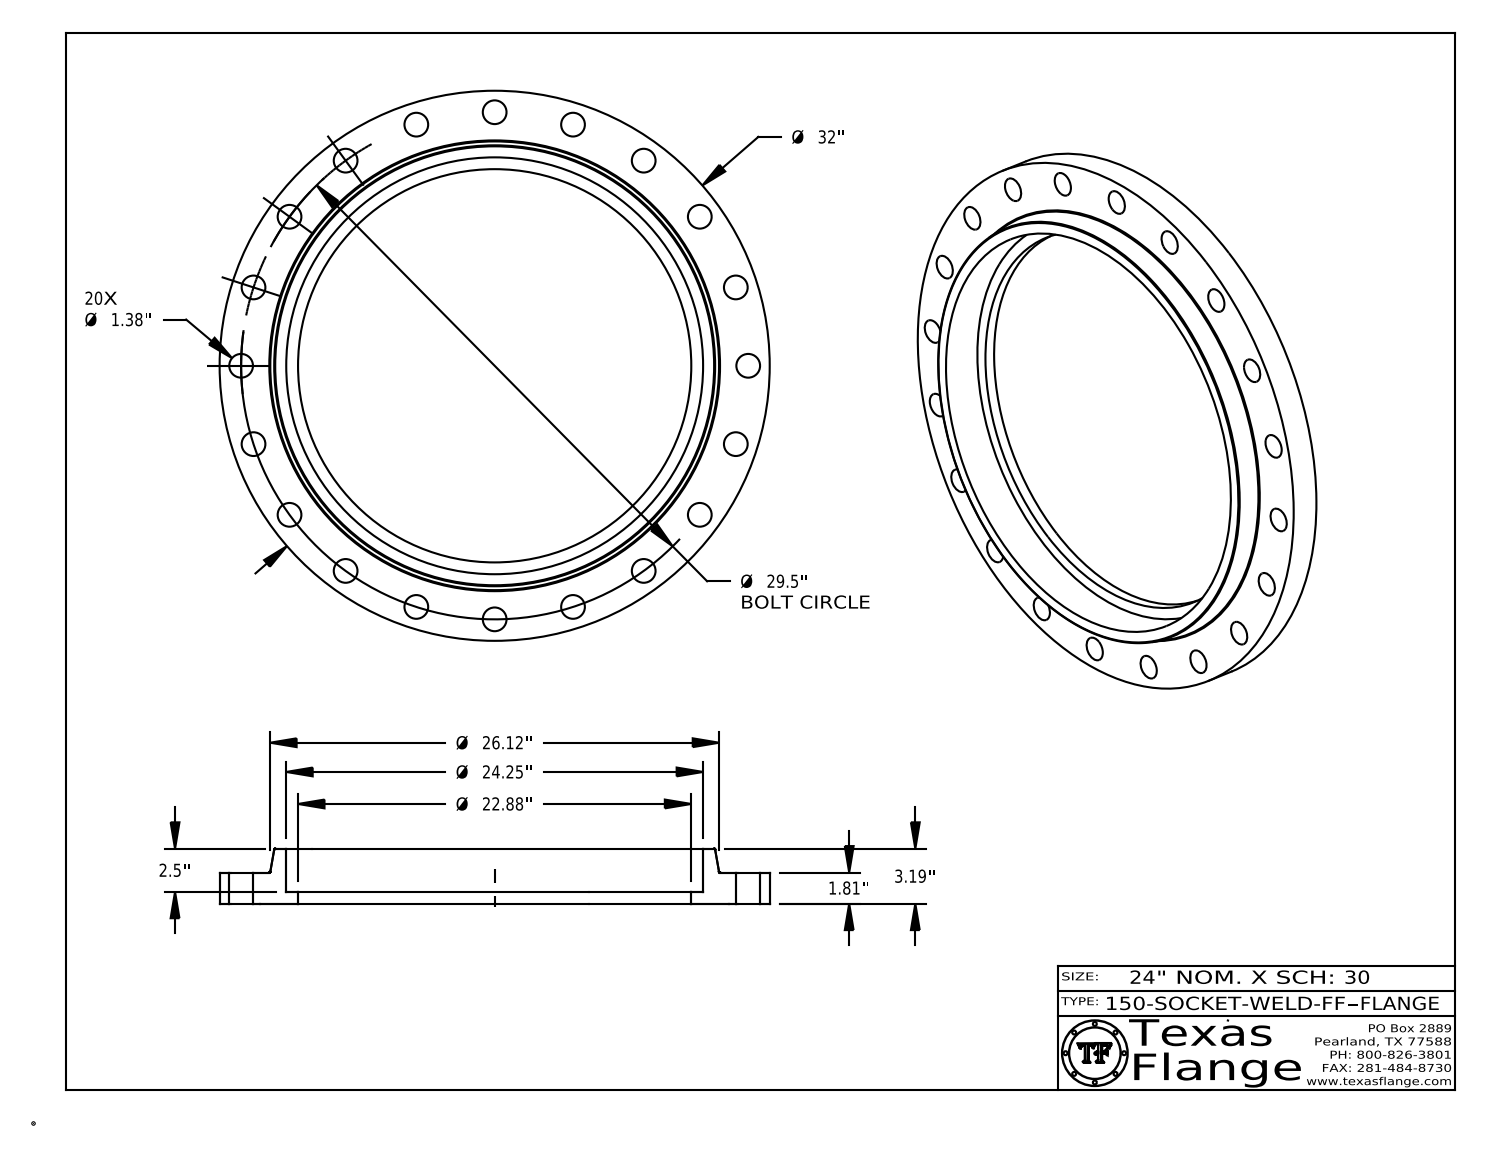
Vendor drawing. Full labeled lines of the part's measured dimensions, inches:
Part name (STEP PRODUCT): 150-SOCKET-WELD-FF
STEP written by: CATIA V5 STEP AP214 (AUTOMOTIVE_DESIGN)
Units: inches
Bodies: 1 solid, 442 faces (370 planar, 66 cylindrical, 6 other)
Overall size (bounding box): 32 × 32 × 3.19
Volume: 689.1 in³ · Surface area: 1 397 in²
Round holes (diameter × count): ⌀1.38 ×20, ⌀0.495 ×1, ⌀22.876 ×1, ⌀24.25 ×1
Round bosses / shafts (diameter × count): ⌀0.03 ×8, ⌀32 ×1, ⌀0.39 ×1
Main face-to-face distances: 1.81, 0.69, 1.12, 3.19, 2.5, 1.38, 1.795, 1.105, 0.015, 1.395
Hole centre spacings: 14.75, 29.137, 4.615, 17.34, 20.859, 23.866, 26.285, 9.116
